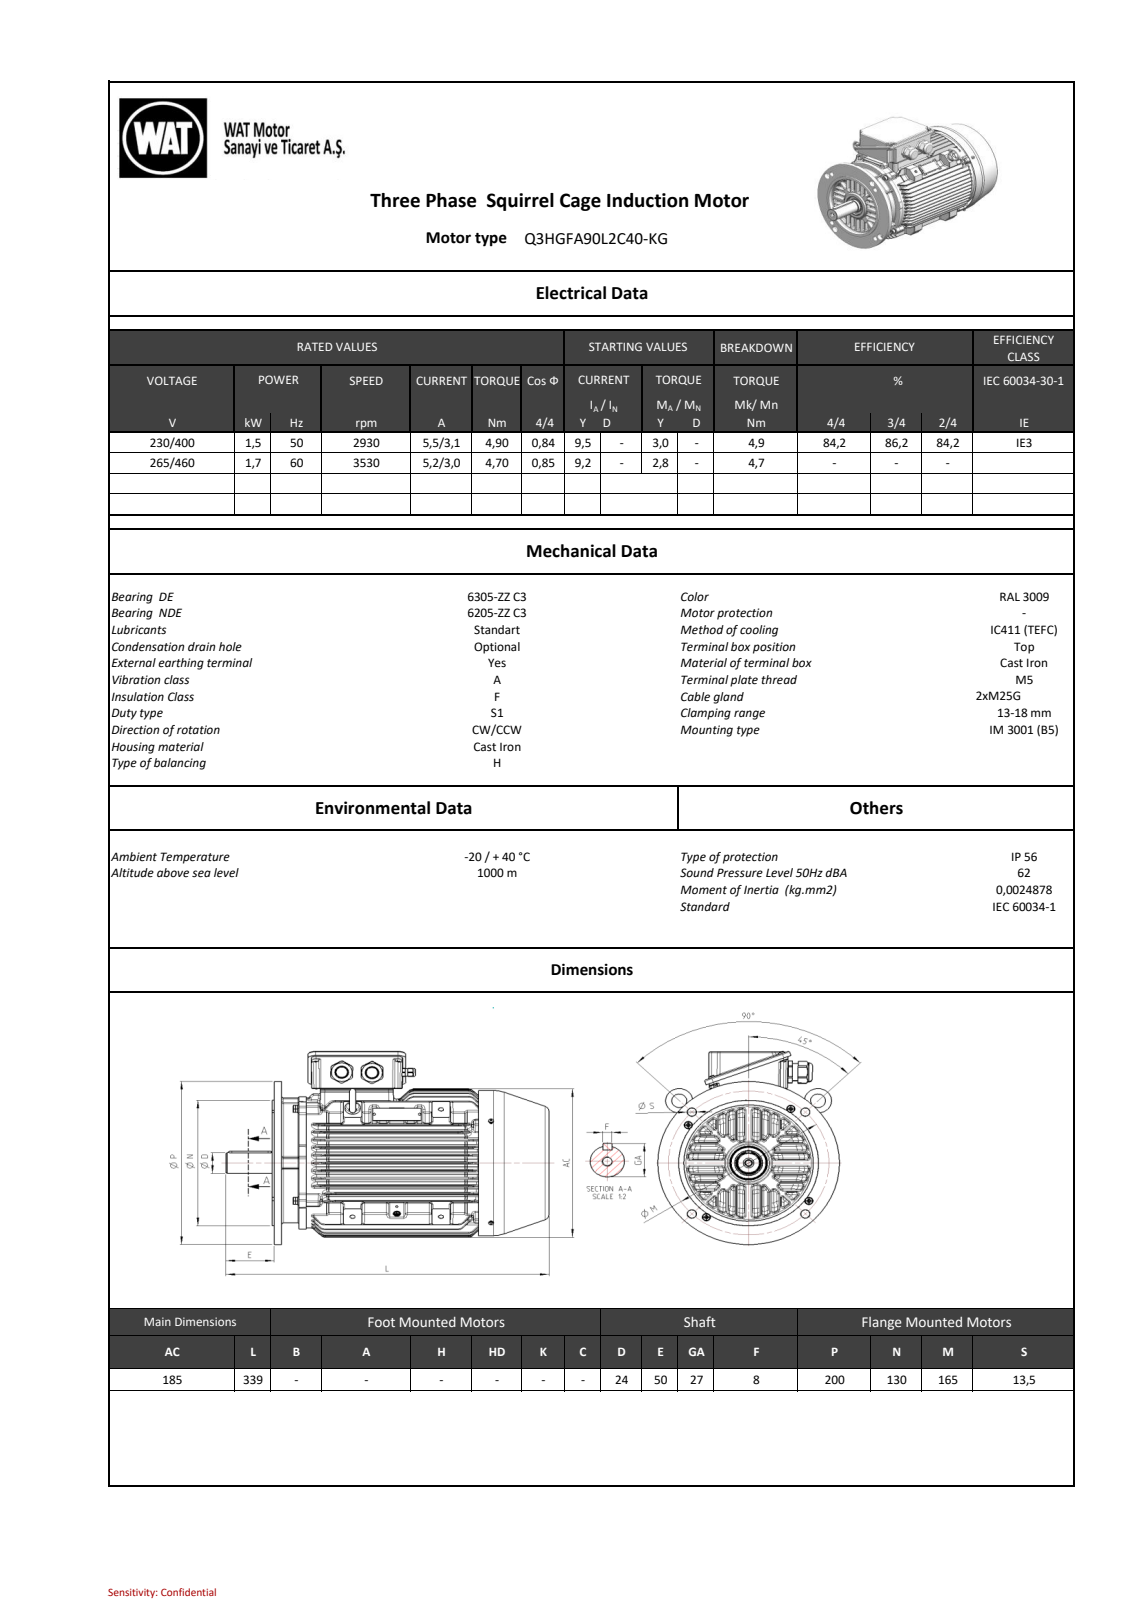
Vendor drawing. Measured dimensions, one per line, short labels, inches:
name: C901B65877A5yip0
written by: SIEMENS PLM Software NX 11.0 (AUTOMOTIVE_DESIGN)
unit: in
bodies: 0 solids, 3001 faces (849 planar, 845 cylindrical, 1307 other)
size: 13.326 × 9.527 × 8.919
holes: 6× ⌀0.394, 4× ⌀0.531, 2× ⌀0.098, 2× ⌀0.677, 1× ⌀0.256, 1× ⌀0.268, 1× ⌀0.331, 1× ⌀1.453, 1× ⌀1.461, 1× ⌀6.85
bosses: 4× ⌀0.787, 3× ⌀0.341, 3× ⌀0.315, 3× ⌀0.197, 2× ⌀1.091, 2× ⌀0.994, 1× ⌀7.874, 1× ⌀6.929
rounds: 312× R0.059, 39× R0.079, 38× R0.157, 28× R0.118, 25× R0.039, 18× R0.047, 12× R0.197, 12× R1.043
face distances: 0.474, 0.256, 9.141, 9.397, 1.96, 11.101, 11.357, 2.464, 0.118, 0.119
hole spacings: 4.593, 3.169, 5.489, 0.841, 3.248, 3.907, 5.091, 5.929
